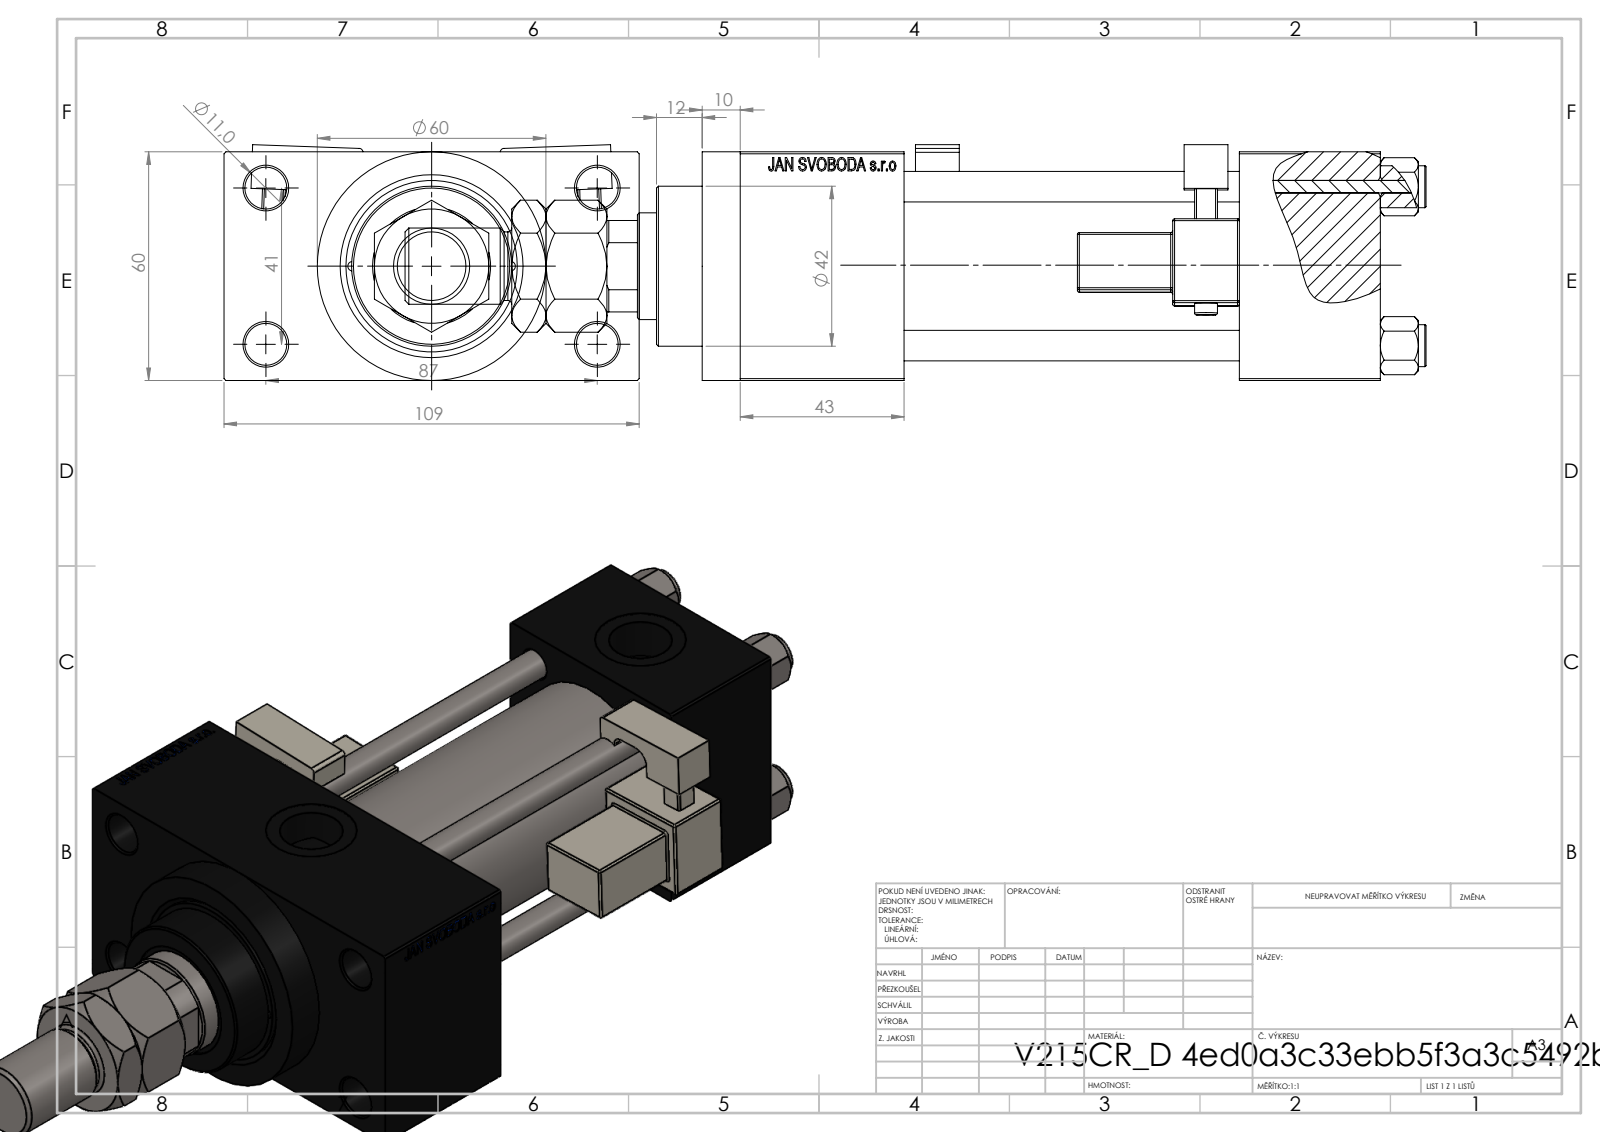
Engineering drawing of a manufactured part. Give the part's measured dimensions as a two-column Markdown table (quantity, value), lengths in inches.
| quantity | value |
| --- | --- |
| part name | V215CR_D_Body; V215CR_VCP_D; V215CR_D_TYCINKA; NUT_M5_D (+3 more) |
| STEP written by | SolidWorks 2019 (CONFIG_CONTROL_DESIGN) |
| units | inches |
| bodies | 14 solids, 1318 faces (575 planar, 157 cylindrical, 586 other) |
| overall size | 10.551 × 4.291 × 2.437 |
| volume | 39.01 in³ |
| surface area | 247.2 in² |
| round holes (diameter × count) | 0.315 × 4, 0.433 × 4, 0.098 × 2, 0.276 × 2, 0.656 × 2, 0.945 × 2, 0.728 × 1, 1.102 × 1, 1.22 × 1, 1.575 × 1, 1.772 × 1 |
| round bosses / shafts (diameter × count) | 0.433 × 4, 0.236 × 2, 2.362 × 1, 1.811 × 1, 1.654 × 1, 0.787 × 1, 0.709 × 1 |
| partial cylindrical surfaces (radius × count) | 0.02 × 48, 0.039 × 2, 0.098 × 2, 0.157 × 2, 0.531 × 1 |
| main face-to-face distances | 2.362, 3.465, 0.965, 3.327, 1.457, 4.921, 5.157, 6.614, 1.693, 4.291 |
| hole center spacings | 0.821, 0.892, 1.161, 1.206, 1.642, 1.832, 1.856, 1.893 |
